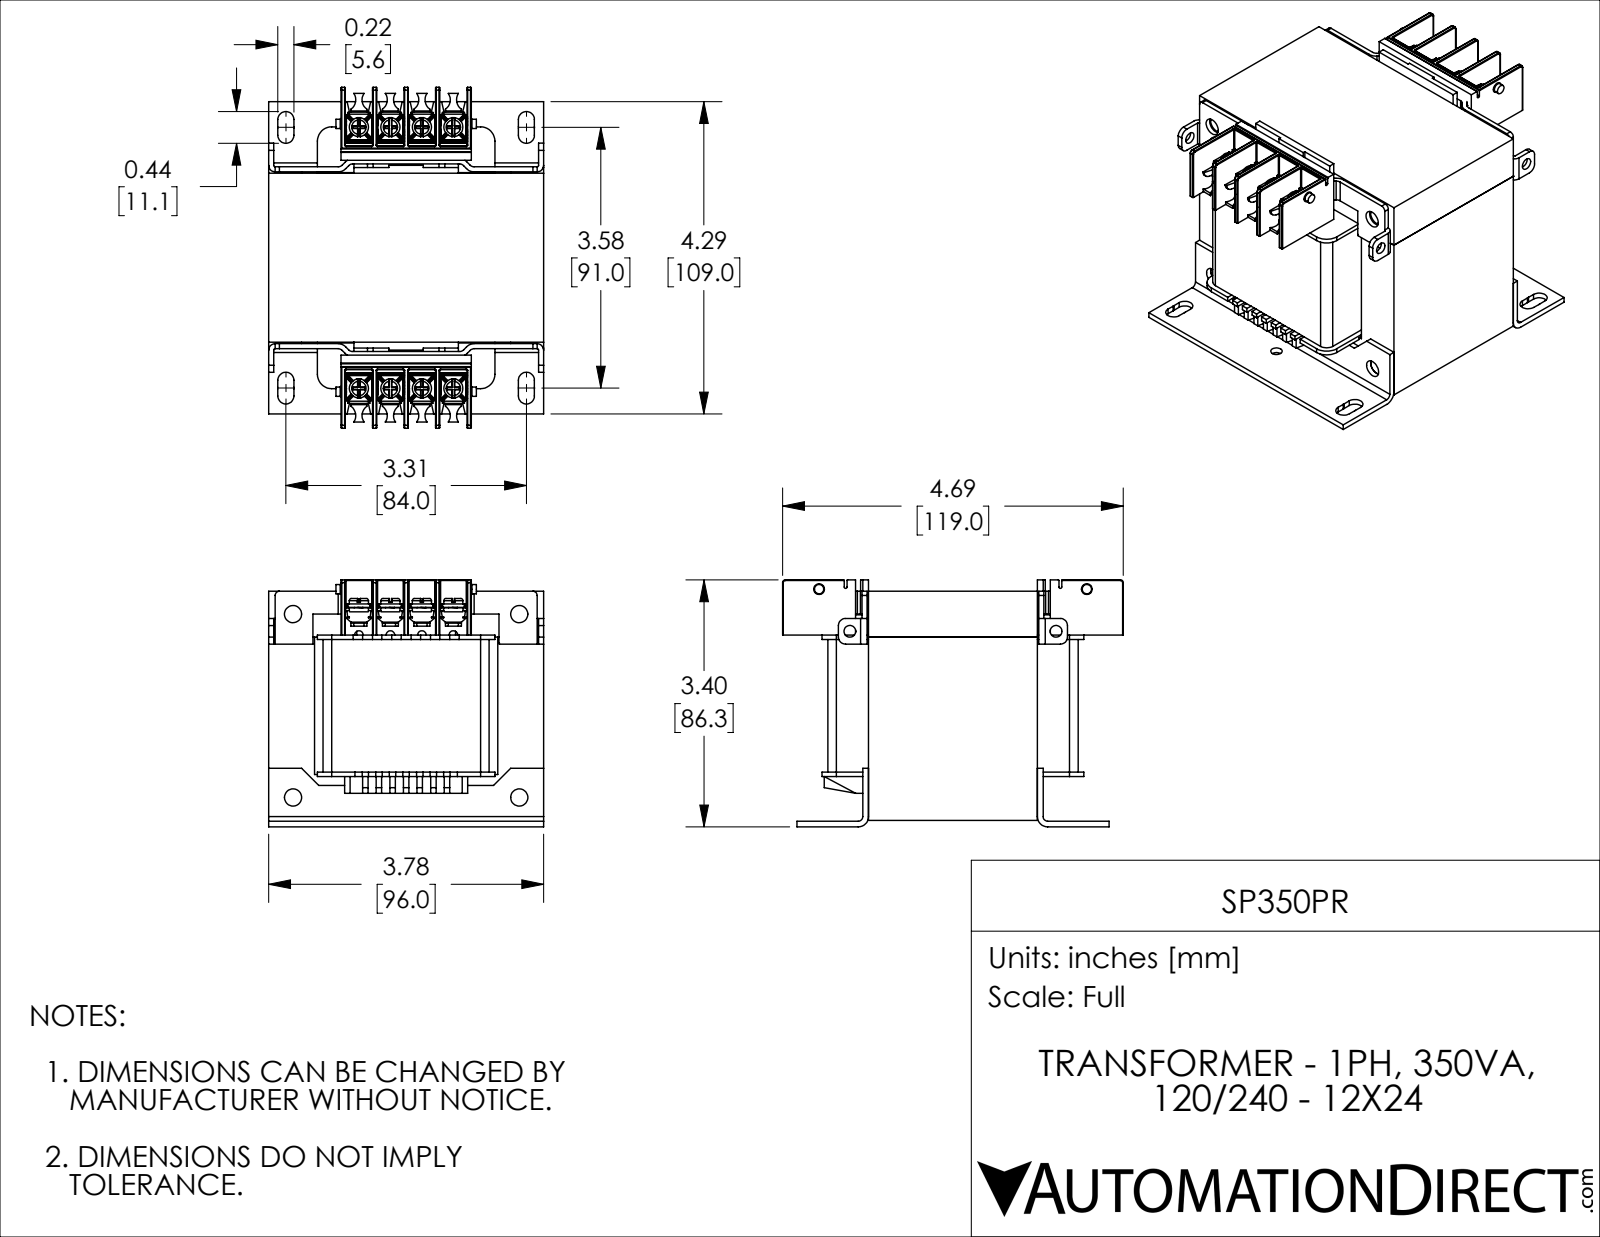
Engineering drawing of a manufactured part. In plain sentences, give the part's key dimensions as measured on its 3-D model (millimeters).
The part is named "SP350PR". Its 3-D file was written by "SolidWorks 2018 (AUTOMOTIVE_DESIGN)". It is 41 solids with 3229 faces: 1997 planar, 934 cylindrical and 298 other. Overall it measures 119 by 96 by 86.3 millimeters. Its volume is 550 100 cubic millimeters and its surface area 142 100 square millimeters. Round holes: 10 of diameter 4, 8 of diameter 2.7, 8 of diameter 3.5, 4 of diameter 6, 2 of diameter 4.1. Round bosses or shafts: 8 of diameter 6.7, 8 of diameter 6.1, 8 of diameter 4.3, 8 of diameter 2.8, 2 of diameter 3.3. Partial cylindrical surfaces (rounded edges, fillets, slot ends): 62 of radius 0.3, 52 of radius 0.1, 42 of radius 0.3, 32 of radius 0.7, 16 of radius 4, 12 of radius 0.9, 12 of radius 1.7, 10 of radius 2. The main face-to-face distances are 16, 64, 80, 61, 32, 2, 59, 48, 19, 77. The hole center spacings are 11, 22, 91.6, 33, 91, 93.6, 91.4, 91.9.
